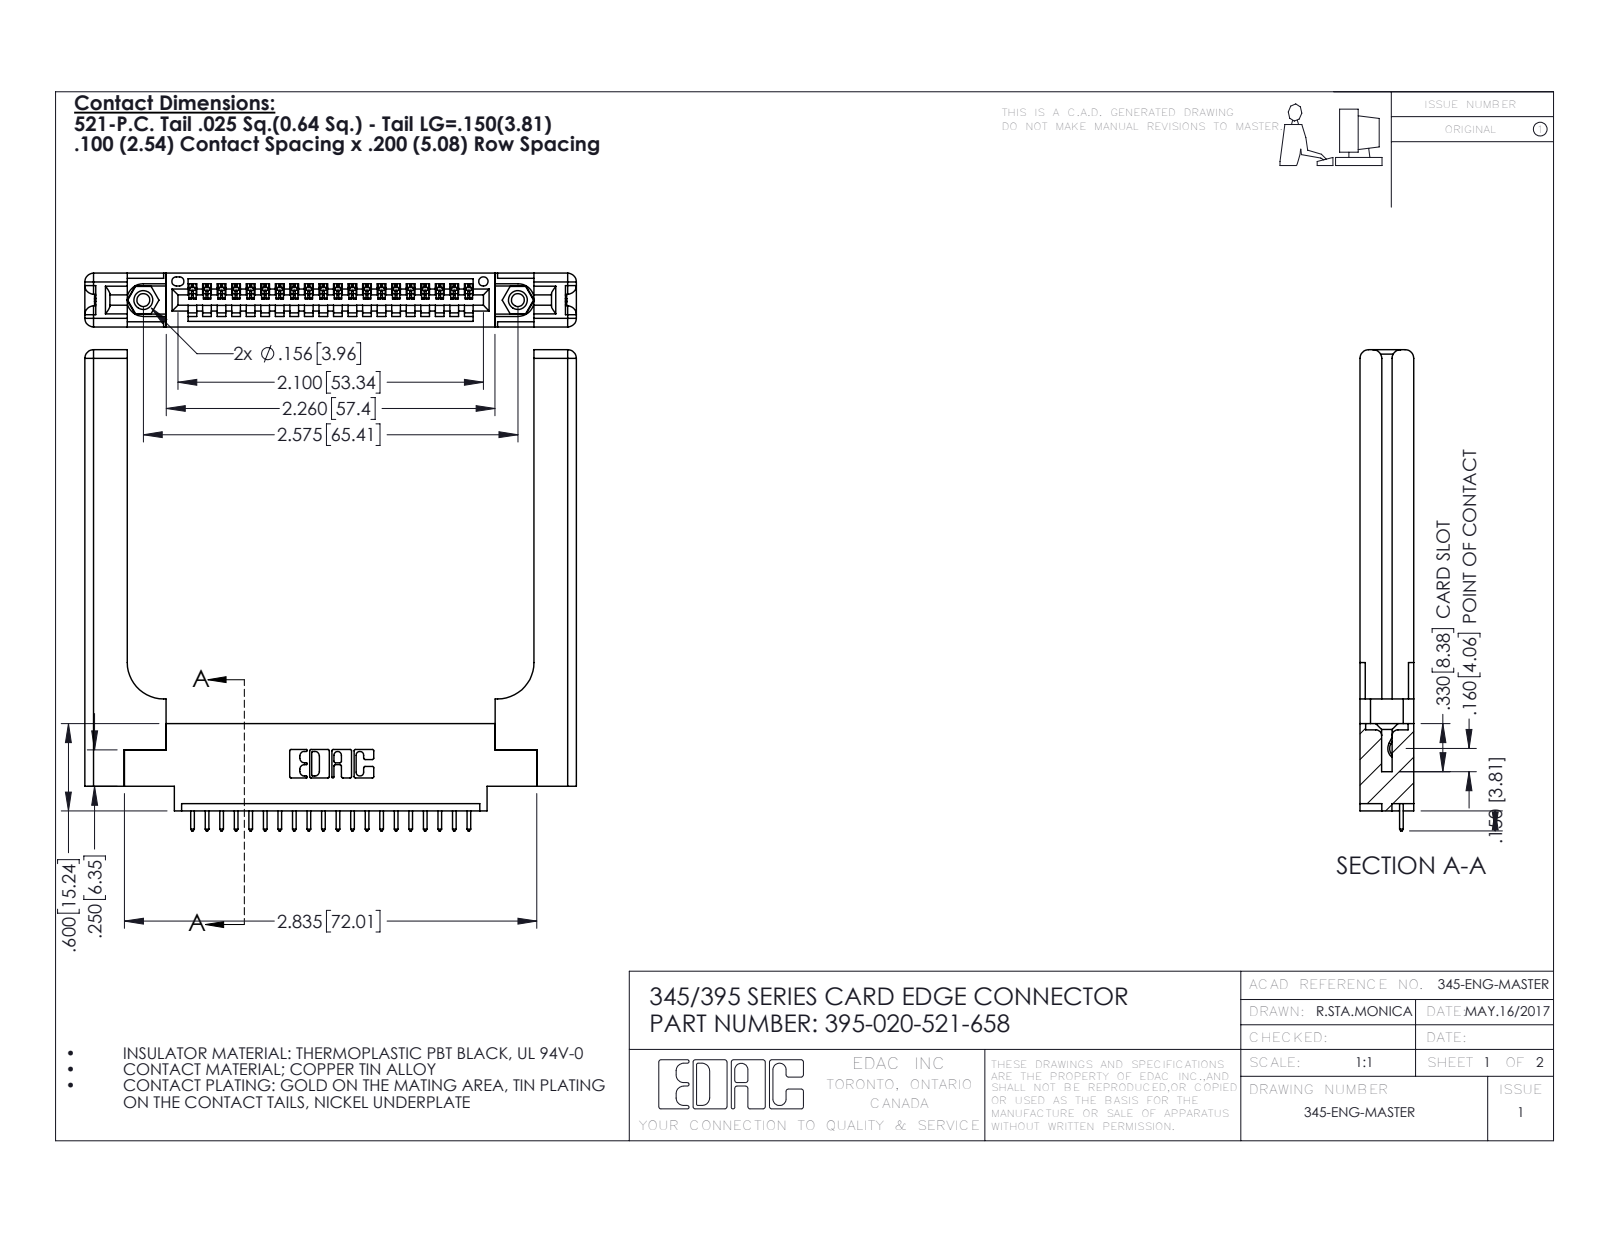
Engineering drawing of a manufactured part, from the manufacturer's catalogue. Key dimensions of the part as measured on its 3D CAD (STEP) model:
Part name (STEP PRODUCT): 345-250-001_345-250-001-102; 395-020-521-658; 345-292-001_345-293-121; 345 Part_0.170 Offset - 0.156 Dia-TH (+1 more)
STEP written by: SolidWorks 2016 (CONFIG_CONTROL_DESIGN)
Units: inches
Bodies: 25 solids, 1546 faces (1032 planar, 454 cylindrical, 60 other)
Overall size (bounding box): 3.379 × 3.307 × 0.37
Volume: 0.995 in³ · Surface area: 23.68 in²
Round holes (diameter × count): ⌀0.089 ×2, ⌀0.125 ×2, ⌀0.156 ×2, ⌀0.064 ×1
Round bosses / shafts (diameter × count): ⌀0.155 ×2
Partial cylindrical surfaces — rounded edges, fillets, slot ends (radius × count): R0.006 ×40, R0.01 ×40, R0.01 ×22, R0.06 ×16, R0.007 ×6, R0.031 ×6, R0.026 ×3, R0.03 ×2
Main face-to-face distances: 0.37, 0.072, 0.298, 0.148, 0.15, 0.077, 0.22, 0.098, 0.272, 0.025
Hole centre spacings: 0.27, 2.341, 2.575
